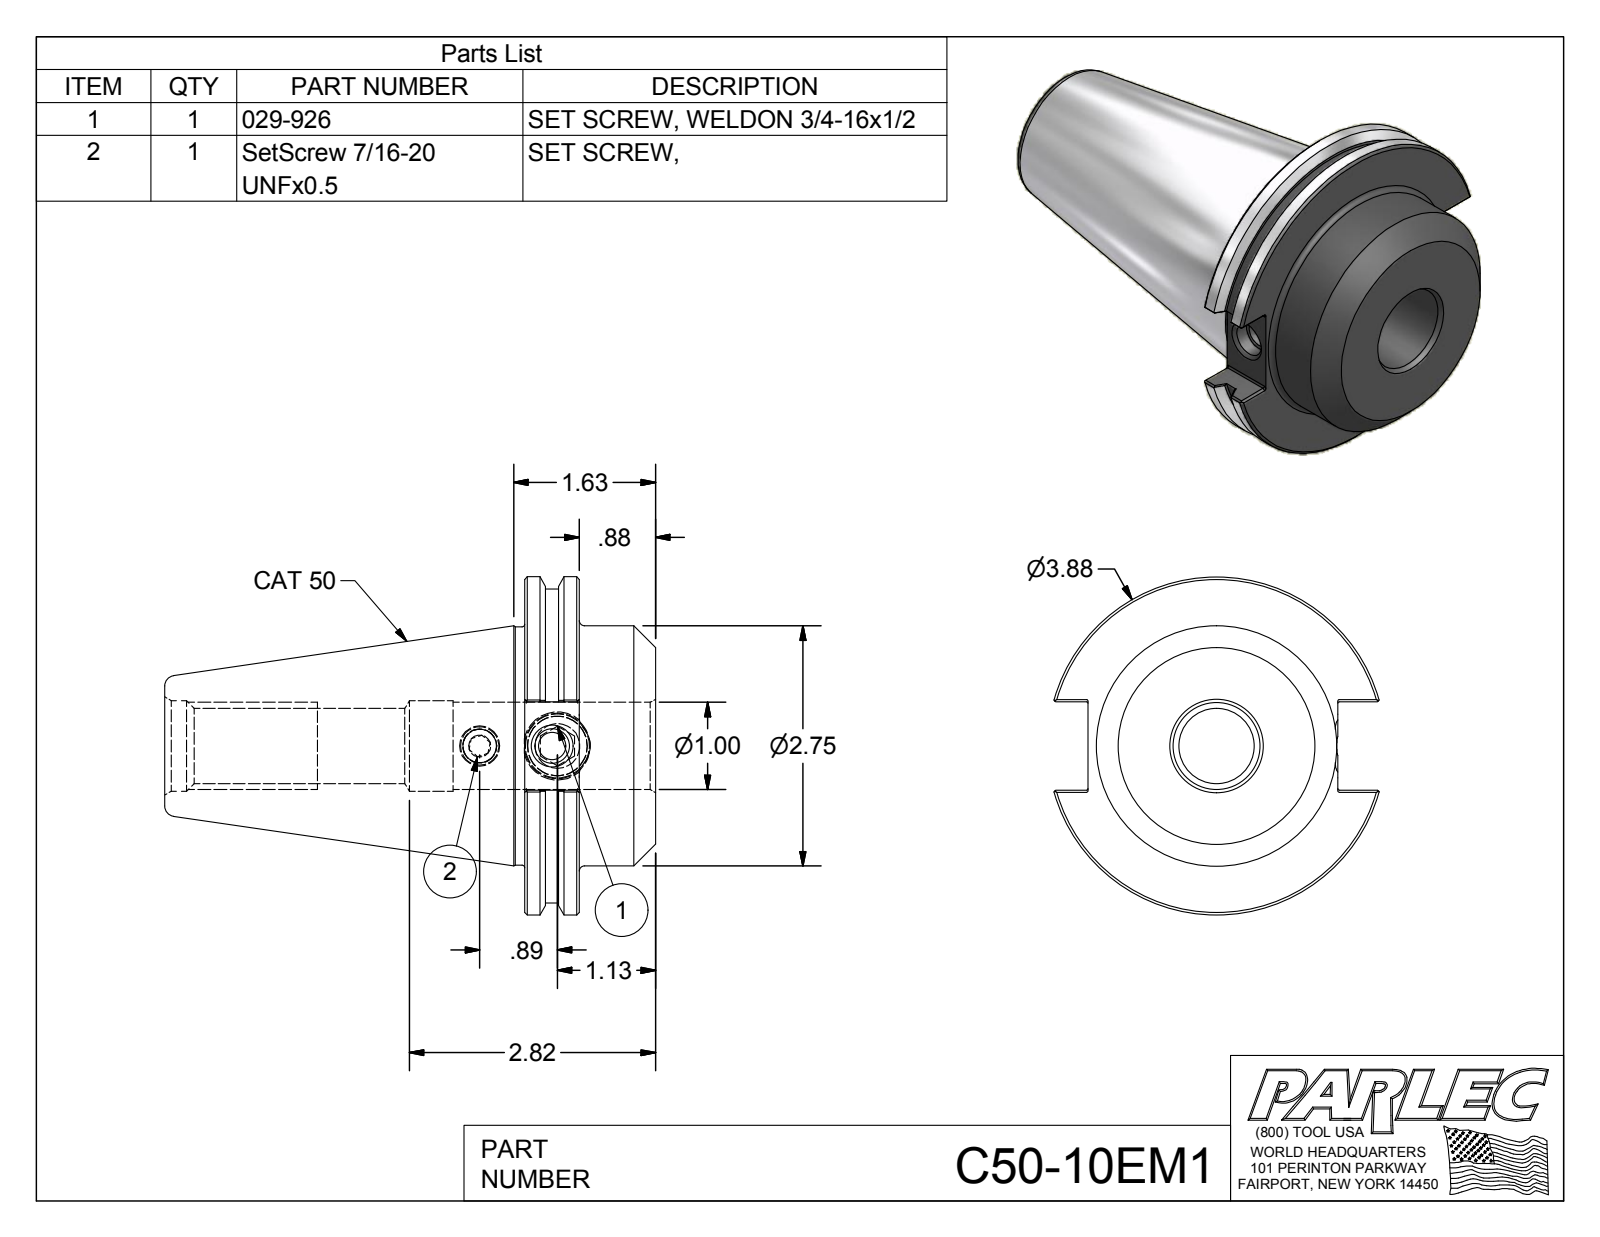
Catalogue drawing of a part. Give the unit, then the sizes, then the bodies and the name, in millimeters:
Units: millimetres
Overall size (bounding box): 142.9 × 98.4 × 94.7
Round holes (diameter × count): ⌀8 ×1, ⌀9.7 ×1, ⌀10.1 ×1, ⌀11.7 ×1, ⌀17.3 ×1, ⌀22 ×1, ⌀25.4 ×1, ⌀26.4 ×1, ⌀26.4 ×1
Round bosses / shafts (diameter × count): ⌀98.4 ×1, ⌀91.3 ×1, ⌀69.9 ×1, ⌀69.3 ×1, ⌀19.1 ×1, ⌀11.1 ×1
Partial cylindrical surfaces — rounded edges, fillets, slot ends (radius × count): R0.5 ×12
Main face-to-face distances: 15.9, 38.1, 22.2, 104.8, 120.7, 142.9, 25.8, 10, 71.4, 110.8
Hole centre spacings: 1.5, 21.1, 22.6
Volume: 376 400 mm³ · Surface area: 53 660 mm²
Bodies: 3 solids, 116 faces (52 planar, 31 cylindrical, 33 other)
Part name (STEP PRODUCT): C50-10EM1; C50-10EM1-1; 029-926; 029-055
STEP written by: Autodesk Inventor 2012 (AUTOMOTIVE_DESIGN)
